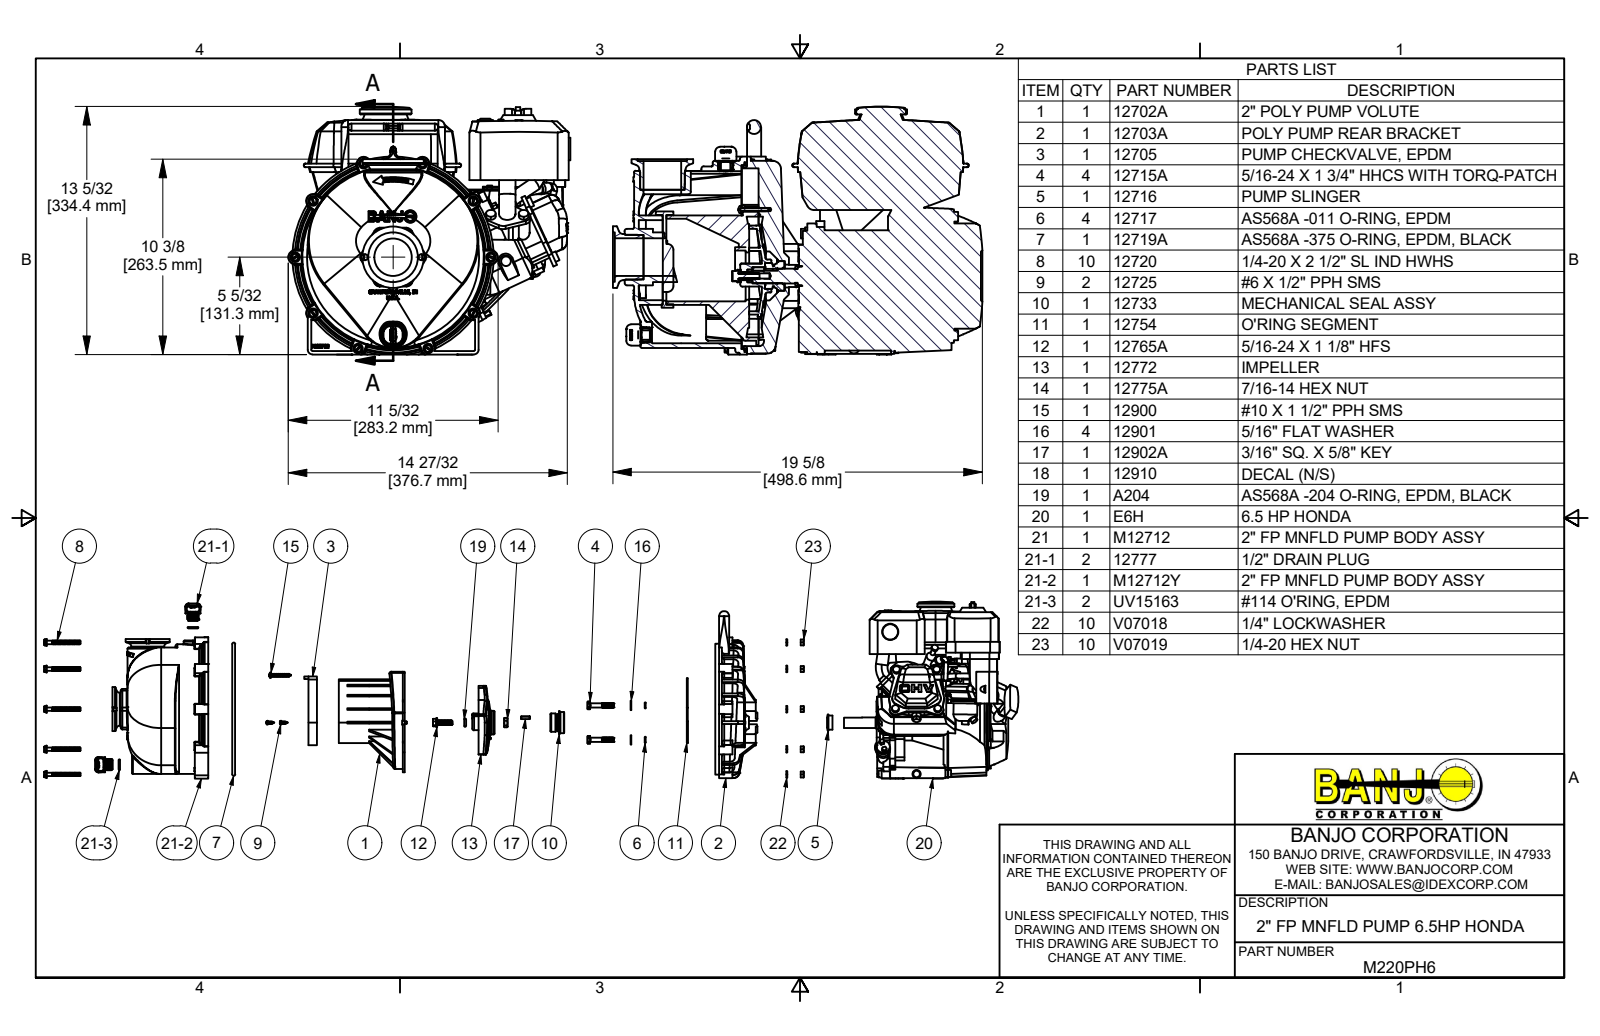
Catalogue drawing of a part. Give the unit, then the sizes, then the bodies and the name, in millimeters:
Units: millimetres
Overall size (bounding box): 517.83 × 380.58 × 334.5
Round holes (diameter × count): ⌀4.98 ×10, ⌀6.4 ×10, ⌀6.86 ×10, ⌀5.59 ×7, ⌀8.73 ×4, ⌀11.91 ×4, ⌀20.7 ×4, ⌀2.87 ×2, ⌀2.92 ×2, ⌀5.21 ×2, ⌀6.35 ×2, ⌀7.87 ×2
Round bosses / shafts (diameter × count): ⌀7.02 ×80, ⌀13.21 ×10, ⌀12.42 ×10, ⌀6.35 ×10, ⌀4.88 ×8, ⌀13 ×6, ⌀17.48 ×4, ⌀7.94 ×4
Partial cylindrical surfaces — rounded edges, fillets, slot ends (radius × count): R0.76 ×117, R6.35 ×33, R1.52 ×25, R4.76 ×25, R2 ×24, R3.17 ×24, R0.38 ×20, R9.53 ×10
Main face-to-face distances: 5.08, 6.35, 25.4, 40.36, 4.13, 15.49, 0.95, 4.58, 7.1, 47.46
Hole centre spacings: 132.08, 79.43, 156.2, 264.16, 45.97, 45.98, 65.01, 65.02
Volume: 19 010 000 mm³ · Surface area: 1 834 000 mm²
Bodies: 88 solids, 8975 faces (2811 planar, 2260 cylindrical, 3904 other)
Part name (STEP PRODUCT): 12703A; M12712X; M17000P; M12712Y (+8 more)
STEP written by: Autodesk Inventor 2015 (AUTOMOTIVE_DESIGN)
